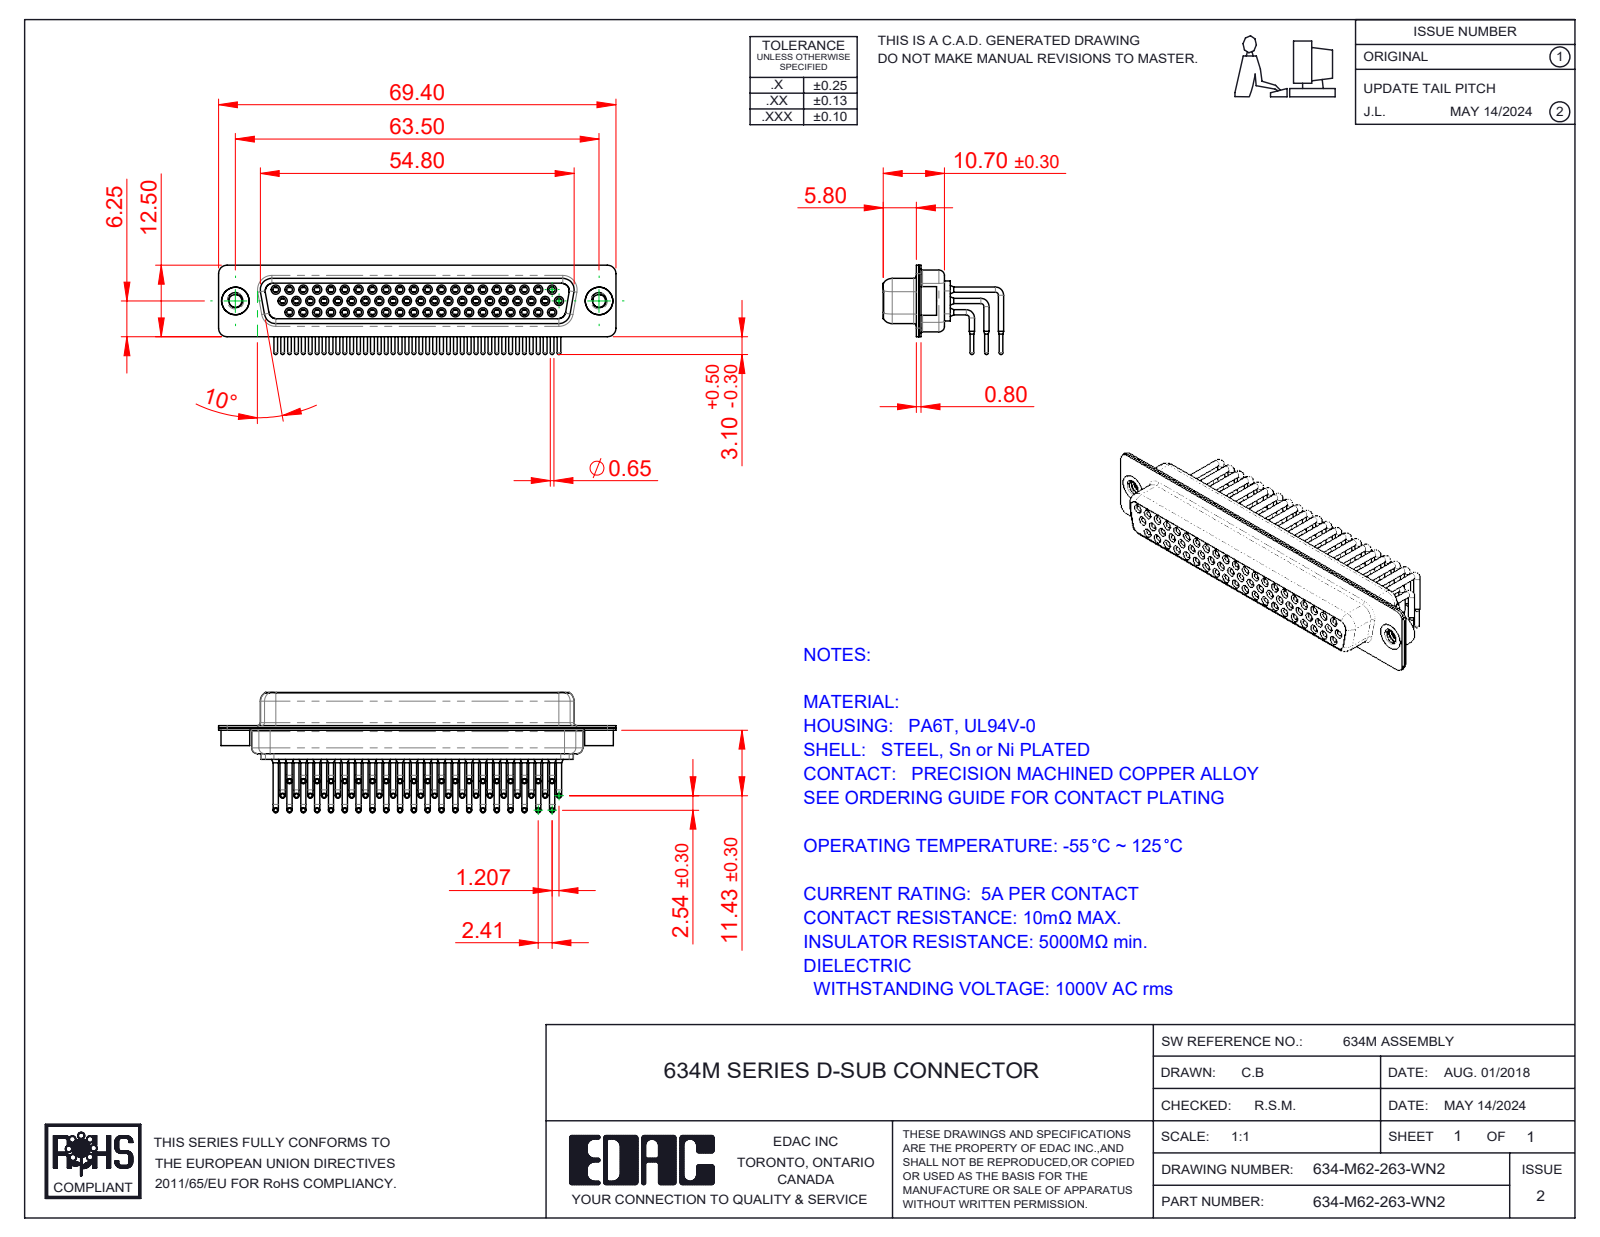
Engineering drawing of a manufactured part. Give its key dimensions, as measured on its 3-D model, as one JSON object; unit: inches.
{"part_name": "634M 4-40 Threaded Rivet; 634-M62-263-WN2; 634M Shell Front_62 Contacts; 634M Contact Row 3 (+4 more)", "step_written_by": "SolidWorks 2016 (CONFIG_CONTROL_DESIGN)", "units": "inches", "bodies": {"solids": 67, "faces": 3565, "planar": 997, "cylindrical": 1563, "other": 1005}, "overall_size": [2.732, 0.828, 0.614], "volume_in3": 0.33, "surface_area_in2": 27.7, "round_holes": [[0.039, 62], [0.043, 62], [0.067, 62], [0.071, 62], [0.079, 62], [0.089, 2], [0.157, 2], [0.189, 2]], "round_bosses_or_shafts": [[0.035, 124], [0.063, 62], [0.059, 62], [0.026, 62], [0.079, 56], [0.197, 2], [0.193, 2]], "partial_cylinders_radius": [[0.059, 16], [0.079, 12], [0.053, 8], [0.063, 8], [0.01, 4], [0.02, 4], [0.024, 4], [0.026, 4]], "face_to_face_distances": [0.016, 0.057, 0.352, 0.075, 0.335, 0.091, 0.244, 0.018, 0.278, 0.033], "hole_center_spacings": [0.285, 0.091, 0.095, 0.38, 0.163, 0.19, 0.665, 0.57]}
